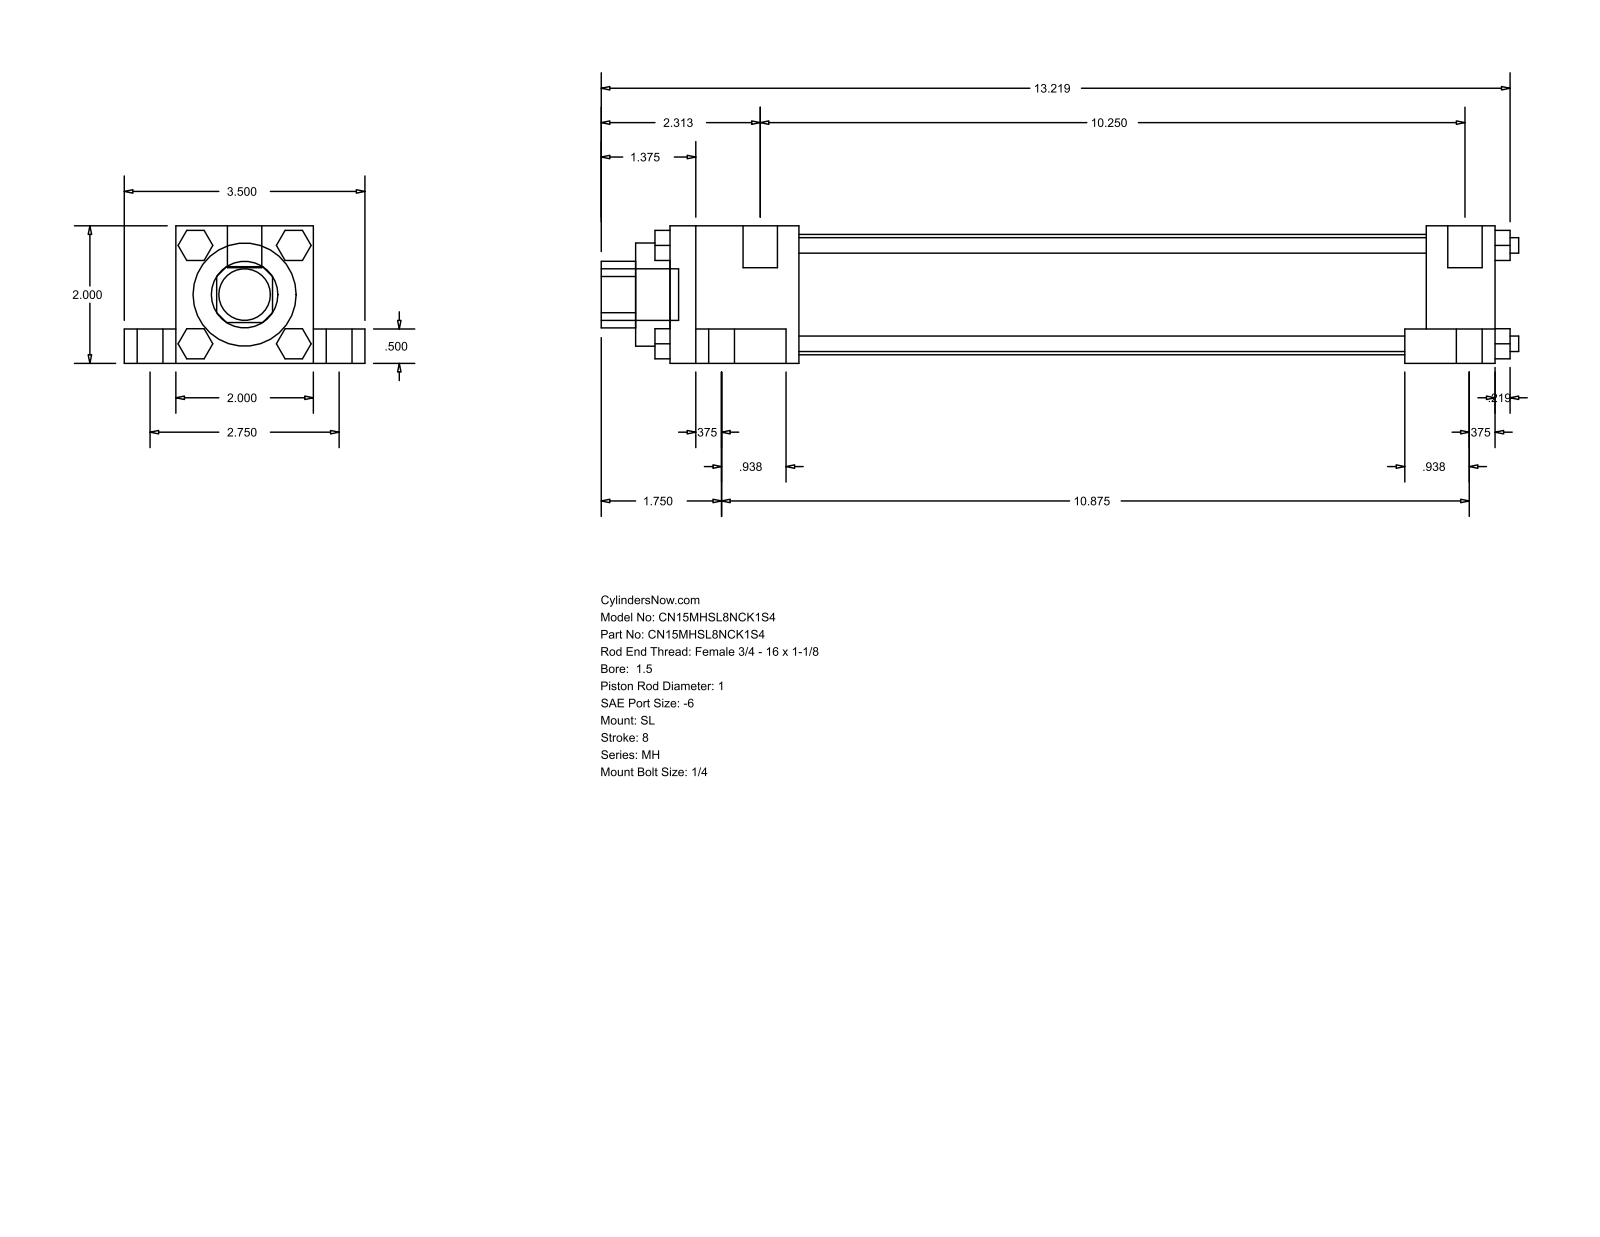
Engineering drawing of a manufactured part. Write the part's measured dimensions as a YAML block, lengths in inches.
part_name: "MH_SL__0150_1"
step_written_by: "GSSL Pune (CONFIG_CONTROL_DESIGN)"
units: inches
bodies: {solids: 0, faces: 148, planar: 112, cylindrical: 36, other: 0}
overall_size: [13.344, 3.5, 2]
round_holes:
  - {diameter: 1, count: 1}
  - {diameter: 1.5, count: 1}
  - {diameter: 1.75, count: 1}
round_bosses_or_shafts:
  - {diameter: 0.625, count: 4}
  - {diameter: 0.375, count: 4}
  - {diameter: 0.225, count: 4}
  - {diameter: 0.219, count: 4}
  - {diameter: 0.5, count: 2}
  - {diameter: 0.75, count: 1}
partial_cylinders:
  - {radius: 0.484, count: 1}
face_to_face_distances: [2, 0.5, 1.5, 0.75, 2.75, 12, 1, 0.375, 1.313, 10.313]
